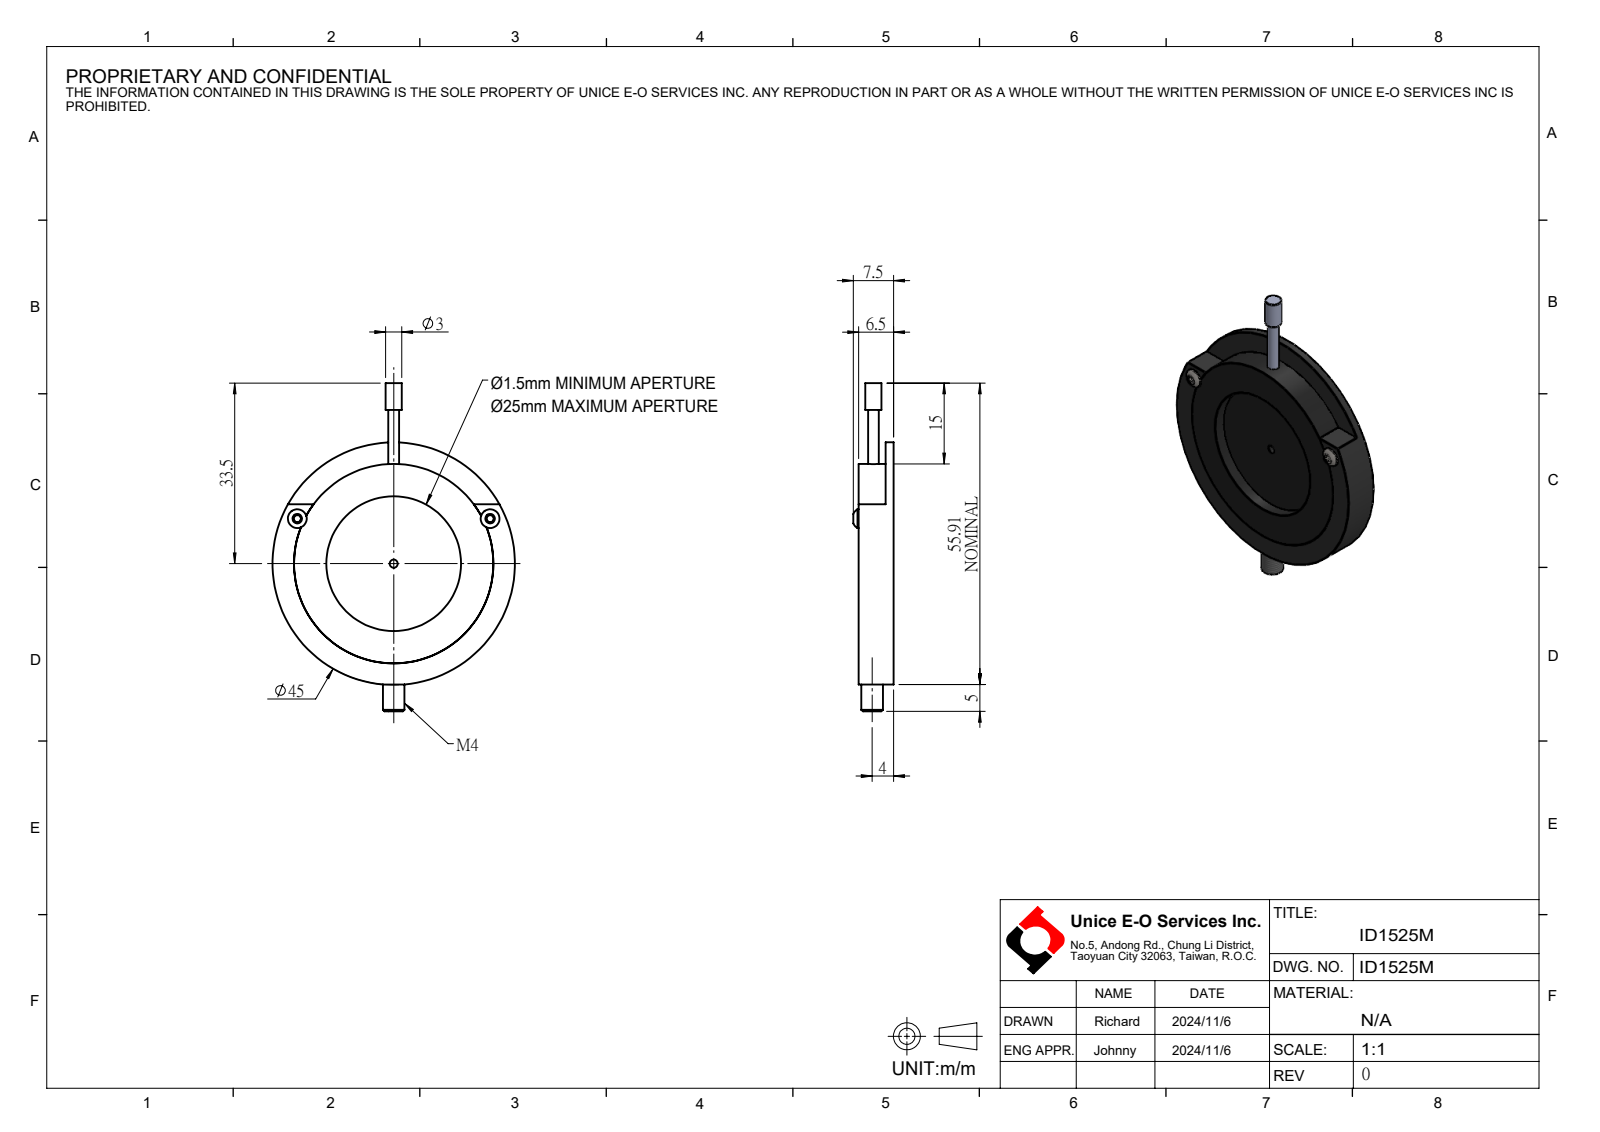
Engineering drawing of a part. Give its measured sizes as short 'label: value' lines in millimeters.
name: ID1525M
written by: SolidWorks 2024 (AUTOMOTIVE_DESIGN)
unit: mm
bodies: 5 solids, 90 faces (43 planar, 35 cylindrical, 12 other)
size: 60.91 × 45 × 7.5
volume: 6 544 mm³; area: 6 253 mm²
holes: 2× ⌀1.6, 1× ⌀1.5, 1× ⌀3.3, 1× ⌀25, 1× ⌀34, 1× ⌀37
bosses: 3× ⌀2, 2× ⌀3.5, 1× ⌀45, 1× ⌀4, 1× ⌀3
face distances: 3.25, 1, 2.25, 5.5, 6.5, 4.25, 5, 1.5, 1.75, 0.5
hole spacings: 19.75, 35.8
